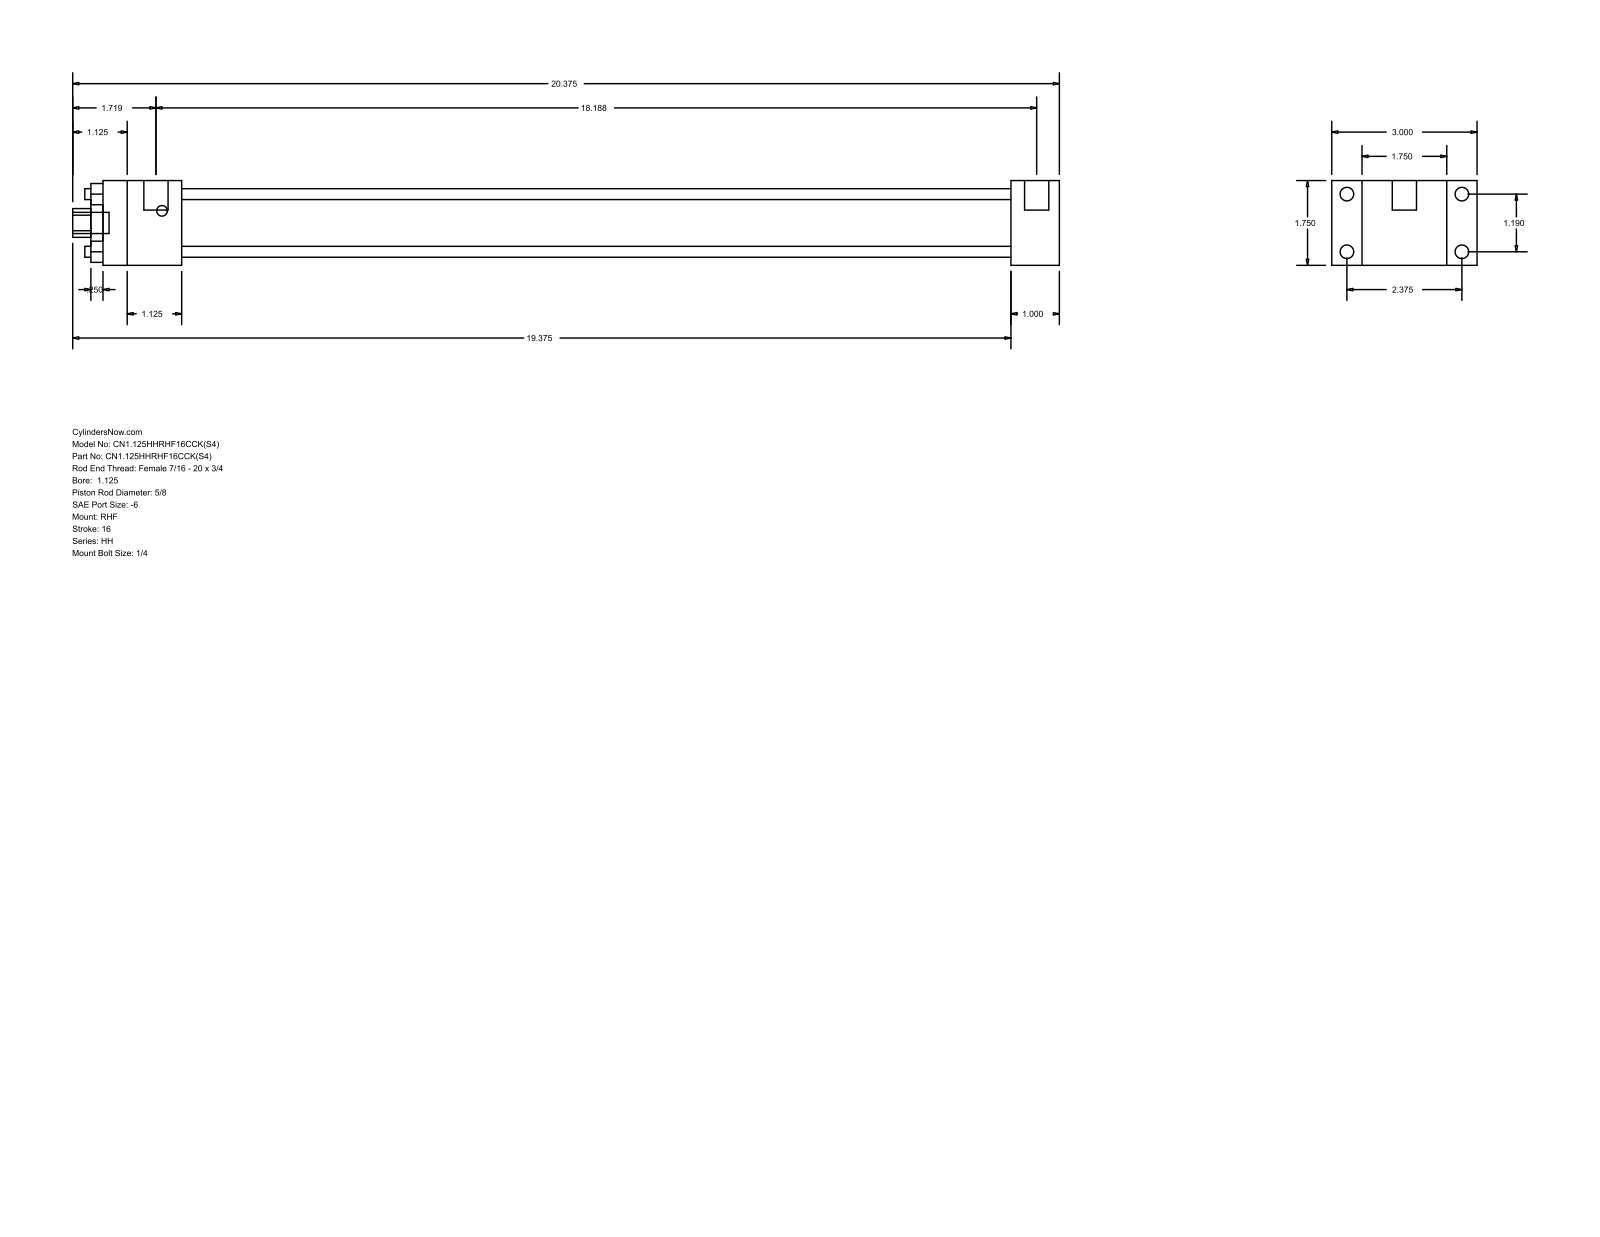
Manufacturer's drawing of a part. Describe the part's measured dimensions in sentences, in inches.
The part is named "HH_RHF__0112_0.625". Its 3-D file was written by "GSSL Pune (CONFIG_CONTROL_DESIGN)". It is 0 solids with 88 faces: 60 planar, 28 cylindrical and 0 other. Overall it measures 20.375 by 3 by 1.75 inches. Round holes: 4 of diameter 0.225, 1 of diameter 0.625, 1 of diameter 1.125, 1 of diameter 1.375. Round bosses or shafts: 4 of diameter 0.281, 4 of diameter 0.219, 2 of diameter 0.5, 1 of diameter 0.437. Partial cylindrical surfaces (rounded edges, fillets, slot ends): 1 of radius 0.297. The main face-to-face distances are 1.75, 0.625, 2.375, 1, 3, 17.125, 18.125, 1.625, 18.75, 19.75. The hole center spacings are 0.841, 1.19, 1.683.
